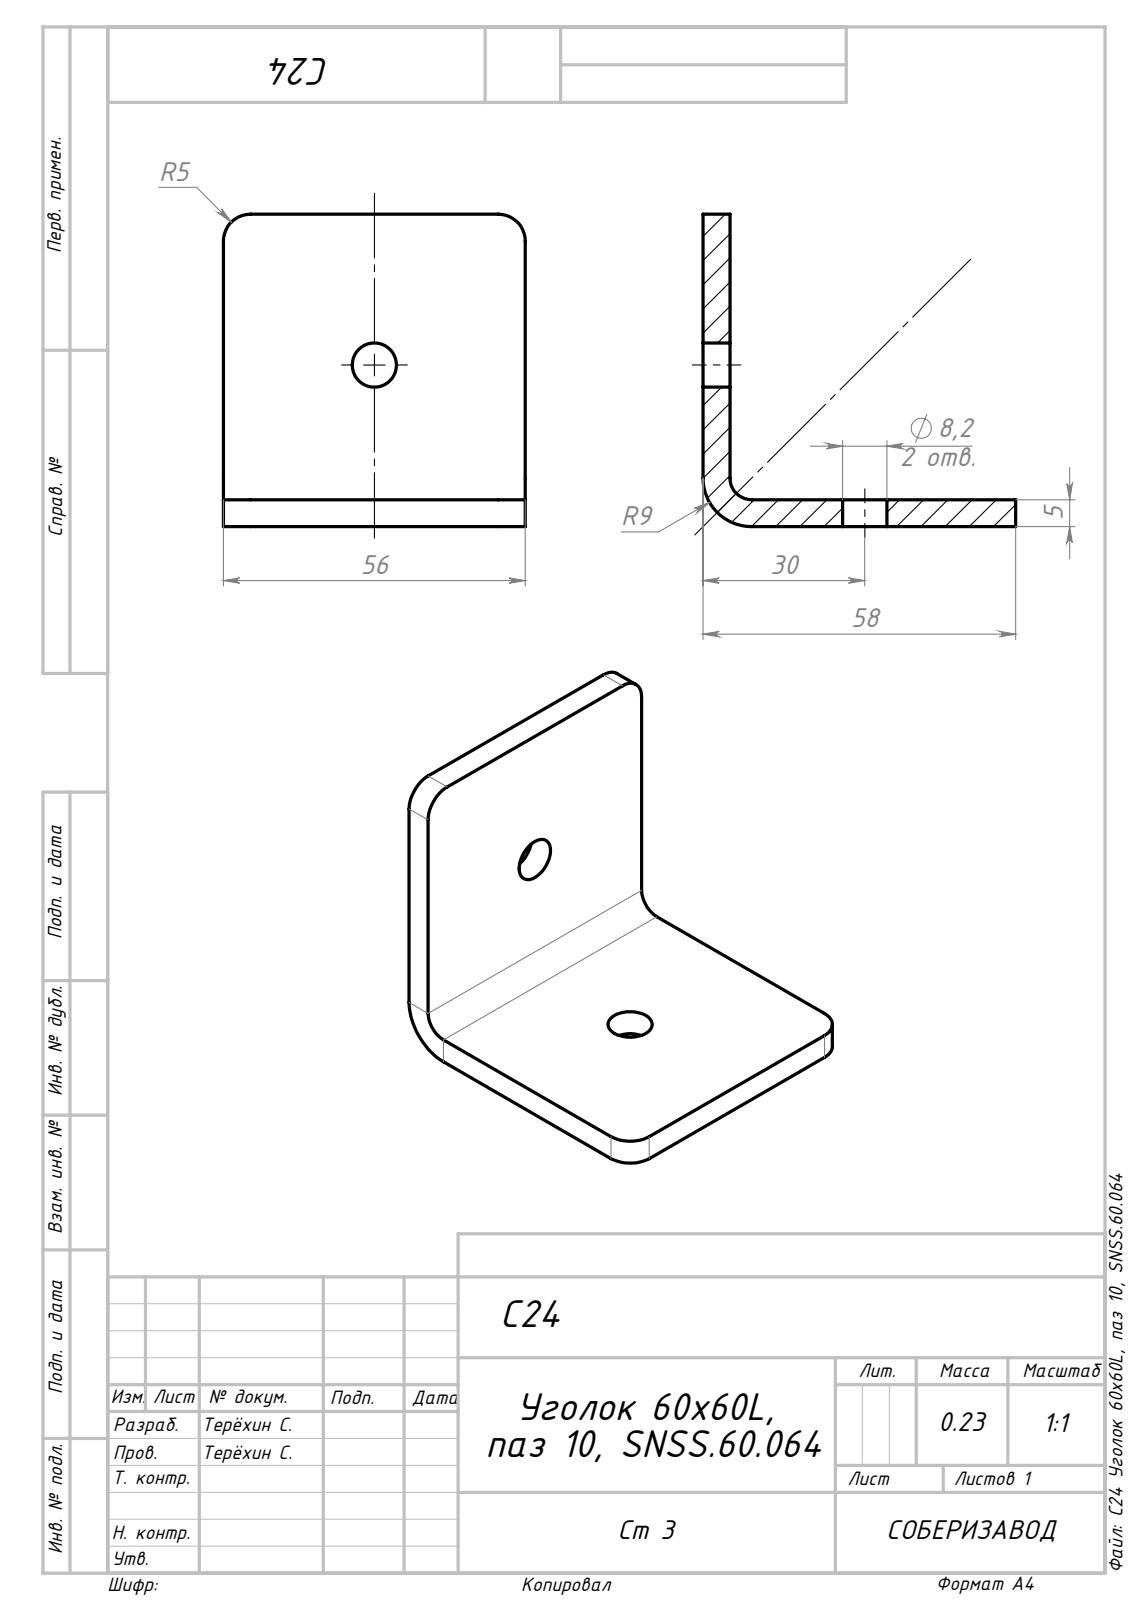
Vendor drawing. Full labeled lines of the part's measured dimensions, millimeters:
Part name (STEP PRODUCT): C24 Уголок 60х60L, паз 10, SNSS.60.064_00; Сборка3
STEP written by: SolidWorks 2022 (AUTOMOTIVE_DESIGN)
Units: millimetres
Bodies: 1 solid, 22 faces (12 planar, 10 cylindrical, 0 other)
Overall size (bounding box): 58 × 58 × 56
Volume: 29 663 mm³ · Surface area: 13 722 mm²
Round holes (diameter × count): ⌀8.2 ×2
Partial cylindrical surfaces — rounded edges, fillets, slot ends (radius × count): R5 ×4, R4 ×1, R9 ×1
Main face-to-face distances: 5, 56, 58, 53
